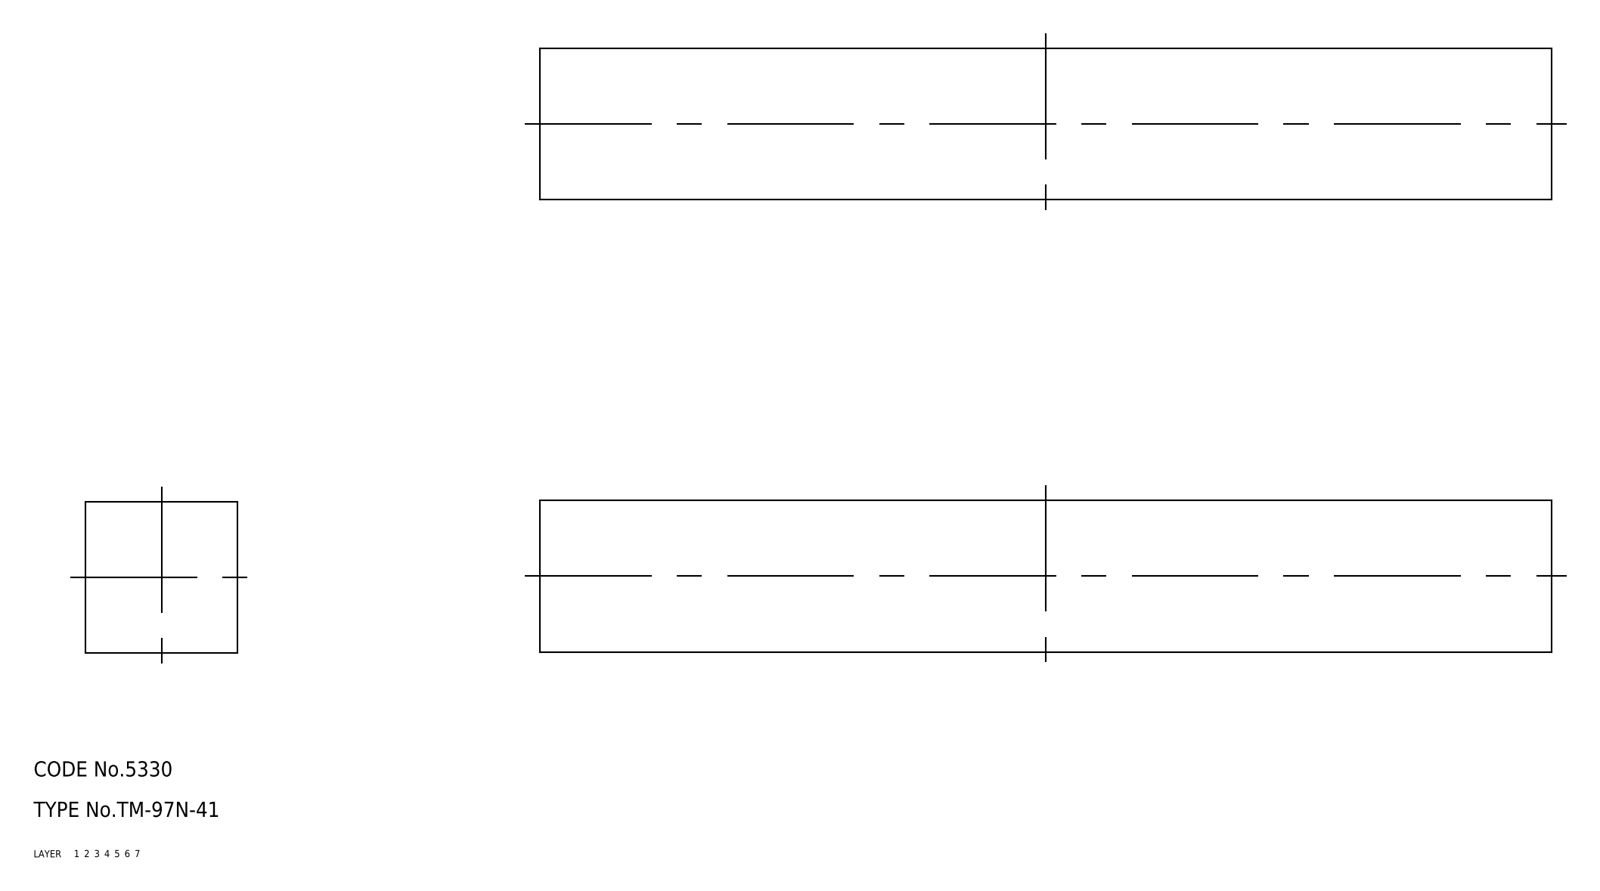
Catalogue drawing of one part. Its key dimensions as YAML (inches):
part_name: "rubber foam"
step_written_by: "CADfix (AUTOMOTIVE_DESIGN)"
units: inches
bodies: {solids: 1, faces: 6, planar: 0, cylindrical: 0, other: 6}
overall_size: [7.874, 1.181, 1.181]
volume: 10.98
surface_area: 39.99
